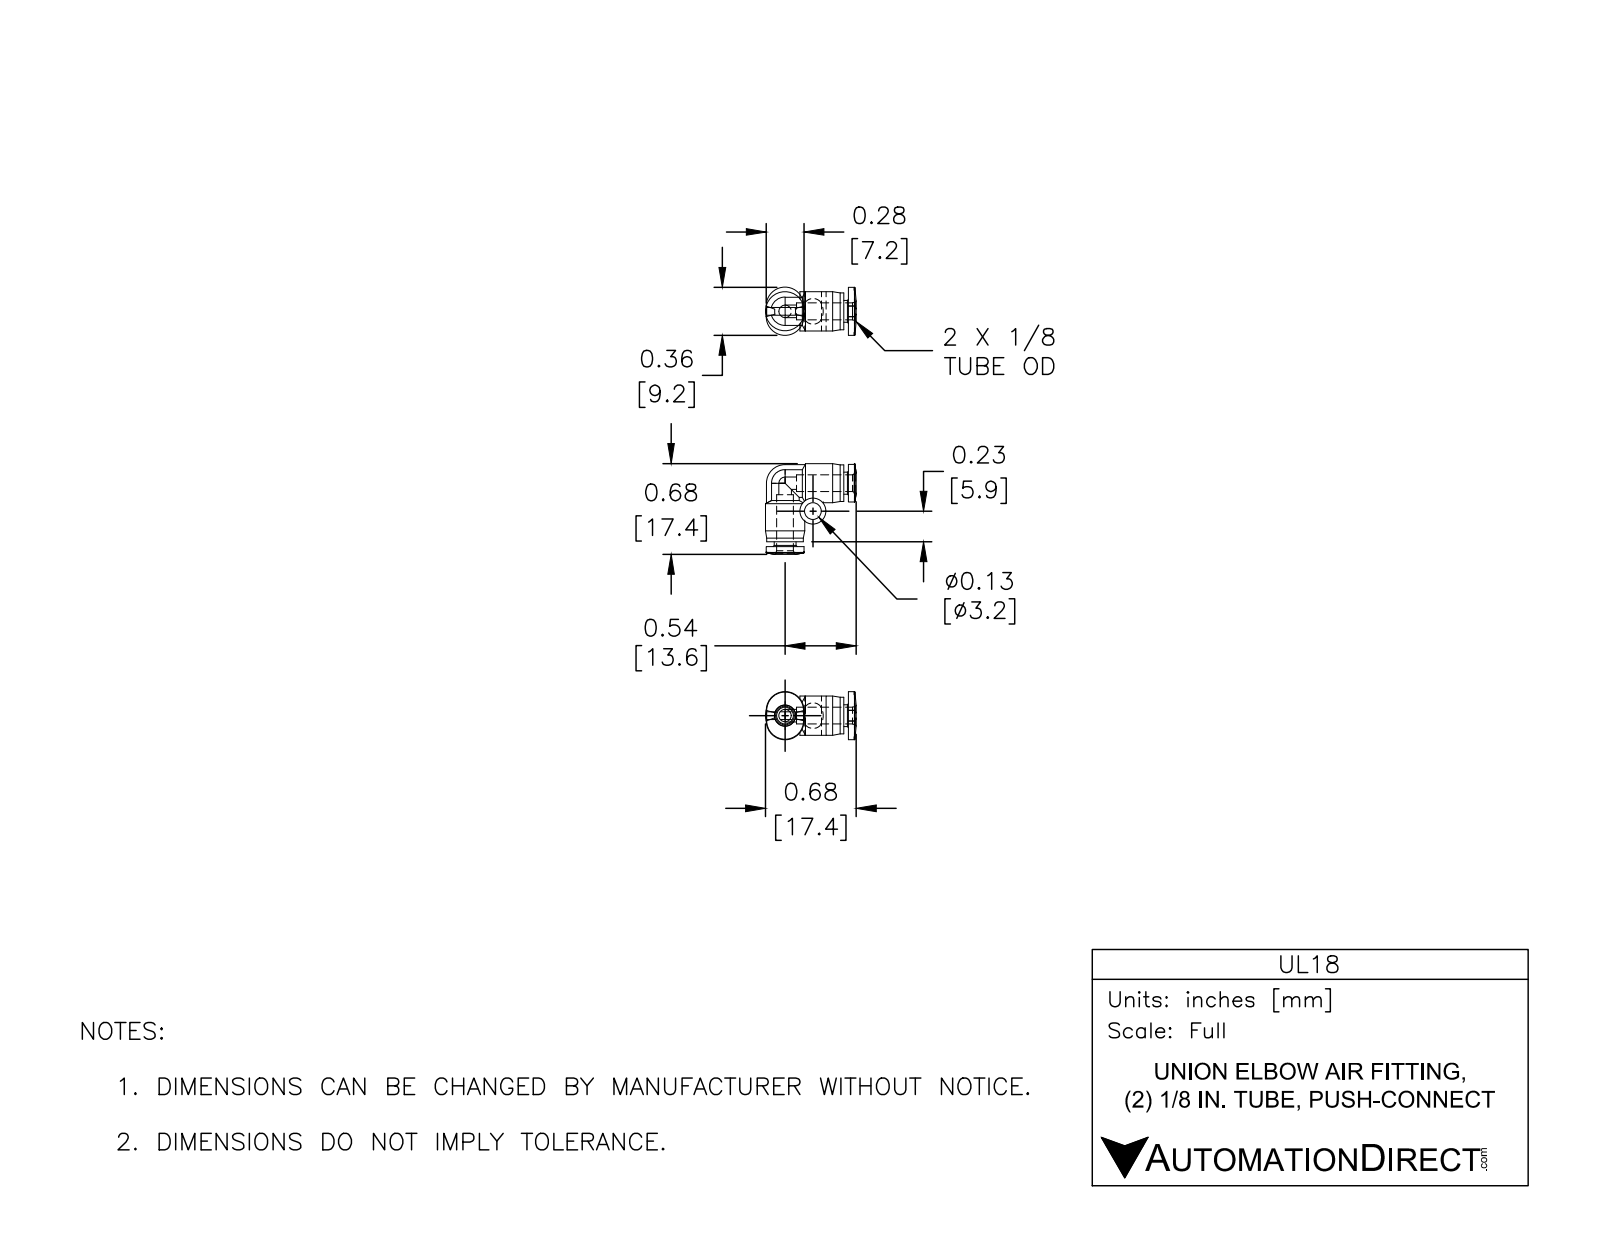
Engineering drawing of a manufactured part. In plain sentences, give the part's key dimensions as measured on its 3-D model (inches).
The part is named "UL18". Its 3-D file was written by "SolidWorks 2015 (CONFIG_CONTROL_DESIGN)". It is 1 solid with 103 faces: 18 planar, 37 cylindrical and 48 other. Overall it measures 0.683 by 0.683 by 0.362 inches. Its volume is 0.053 cubic inches and its surface area 1.931 square inches. Round holes: 3 of diameter 0.126, 2 of diameter 0.094. Round bosses or shafts: 2 of diameter 0.295, 2 of diameter 0.276, 2 of diameter 0.213, 2 of diameter 0.165, 1 of diameter 0.197. Partial cylindrical surfaces (rounded edges, fillets, slot ends): 4 of radius 0.142, 1 of radius 0.14. The main face-to-face distances are 0.035, 0.118, 0.177, 0.059, 0.295, 0.581, 0.616, 0.226, 0.354, 0.39.
